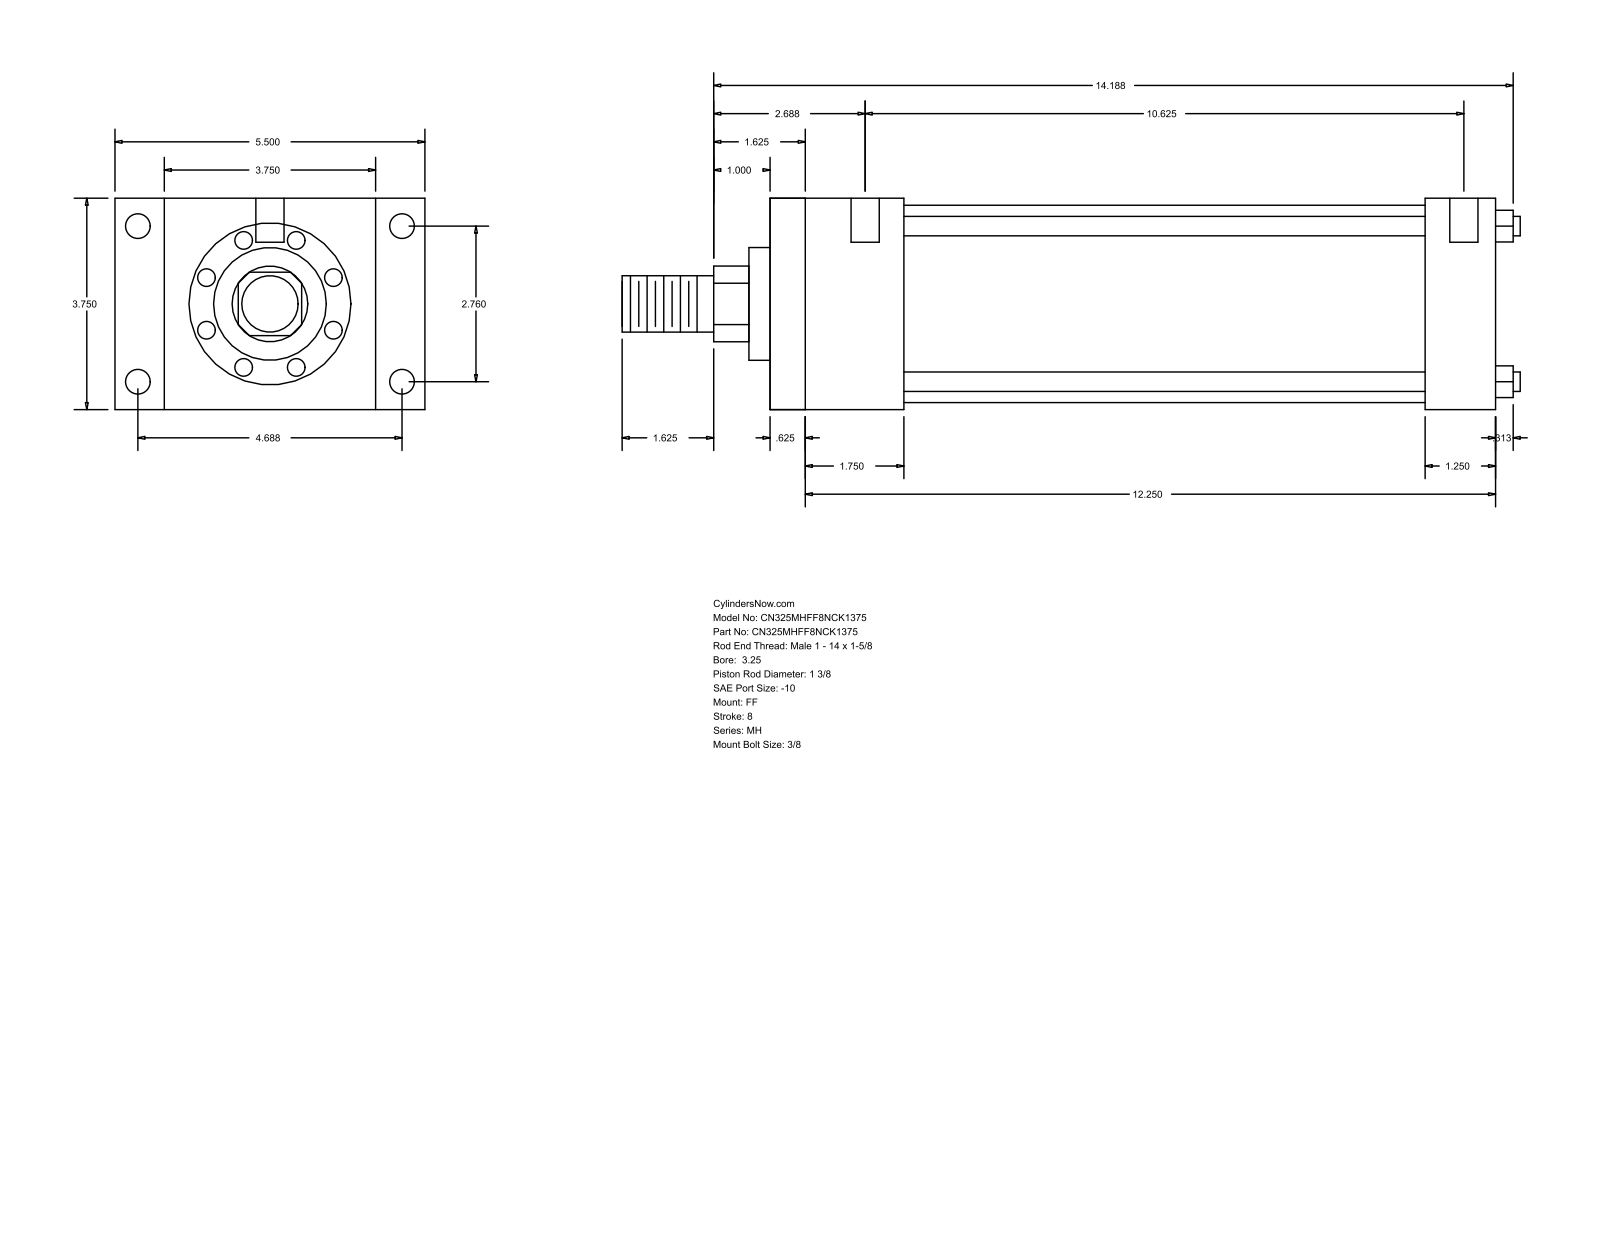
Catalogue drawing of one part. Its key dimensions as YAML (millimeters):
part_name: "MH_FF__0325_1.375"
step_written_by: "GSSL Pune (CONFIG_CONTROL_DESIGN)"
units: millimeters
bodies: {solids: 0, faces: 92, planar: 64, cylindrical: 28, other: 0}
overall_size: [404.81, 139.7, 95.25]
round_holes:
  - {diameter: 5.56, count: 4}
  - {diameter: 11.13, count: 4}
  - {diameter: 12.7, count: 2}
round_bosses_or_shafts:
  - {diameter: 8.76, count: 4}
  - {diameter: 88.9, count: 1}
  - {diameter: 50.8, count: 1}
  - {diameter: 34.92, count: 1}
  - {diameter: 25.4, count: 1}
partial_cylinders:
  - {radius: 17.06, count: 1}
face_to_face_distances: [95.24, 327.03, 15.87, 311.16, 22.23, 117.47, 295.28, 279.41, 31.75, 60.32]
hole_center_spacings: [70.1, 119.06, 138.16, 276.23, 1.59, 4.76, 269.88, 271.47]
